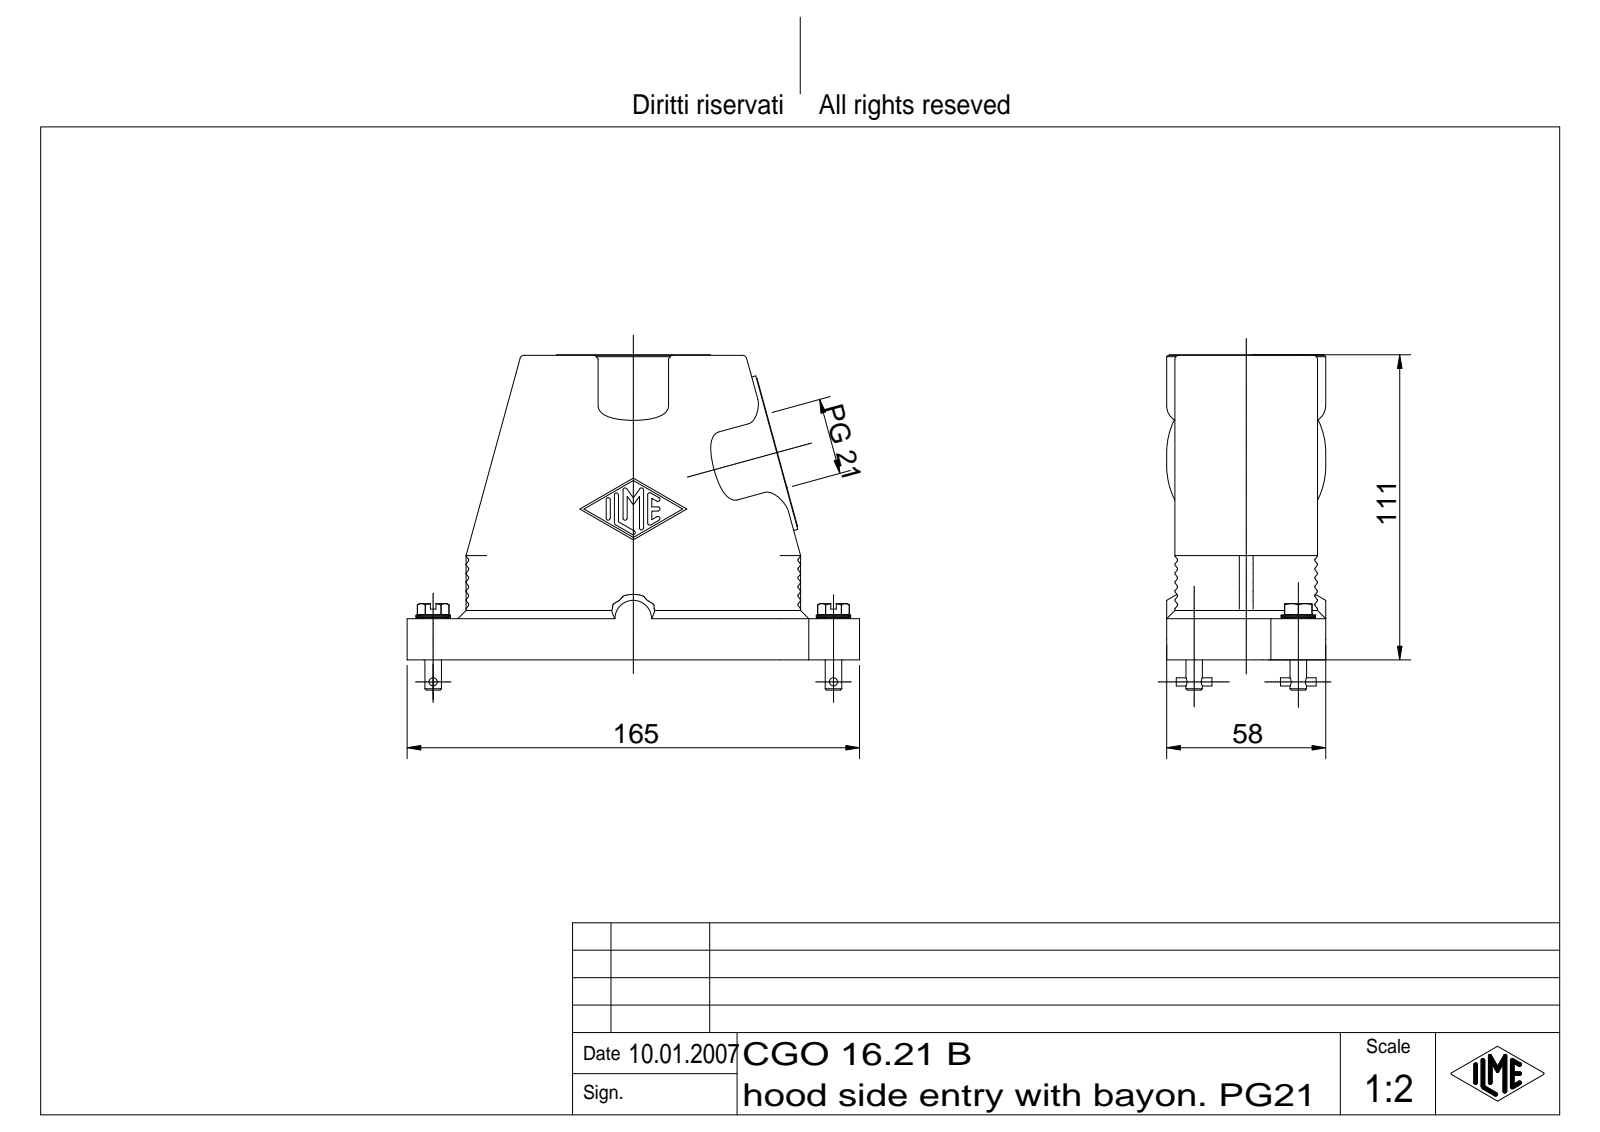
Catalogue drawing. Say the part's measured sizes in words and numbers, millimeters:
The part is named "CGO 16.21 B". Its 3-D file was written by "Autodesk Inventor 7 (AUTOMOTIVE_DESIGN)". It is 3 solids with 779 faces: 193 planar, 203 cylindrical and 383 other. Overall it measures 165 by 122.2 by 58 millimeters. Its volume is 238 558 cubic millimeters and its surface area 91 688 square millimeters. Round holes: 2 of diameter 2.46, 2 of diameter 3.2, 2 of diameter 6.6, 2 of diameter 15, 1 of diameter 26.78. Round bosses or shafts: 2 of diameter 58, 2 of diameter 56, 2 of diameter 12.5, 2 of diameter 6, 2 of diameter 3. Partial cylindrical surfaces (rounded edges, fillets, slot ends): 39 of radius 0.5, 14 of radius 0.75, 8 of radius 7.5, 6 of radius 6, 4 of radius 1.5, 4 of radius 3, 2 of radius 5.75, 2 of radius 10.5. The main face-to-face distances are 3, 52, 49, 6, 46, 55, 2.5, 0.5, 58, 3.5. The hole center spacings are 34.69, 116.38, 82.07, 150.86.
